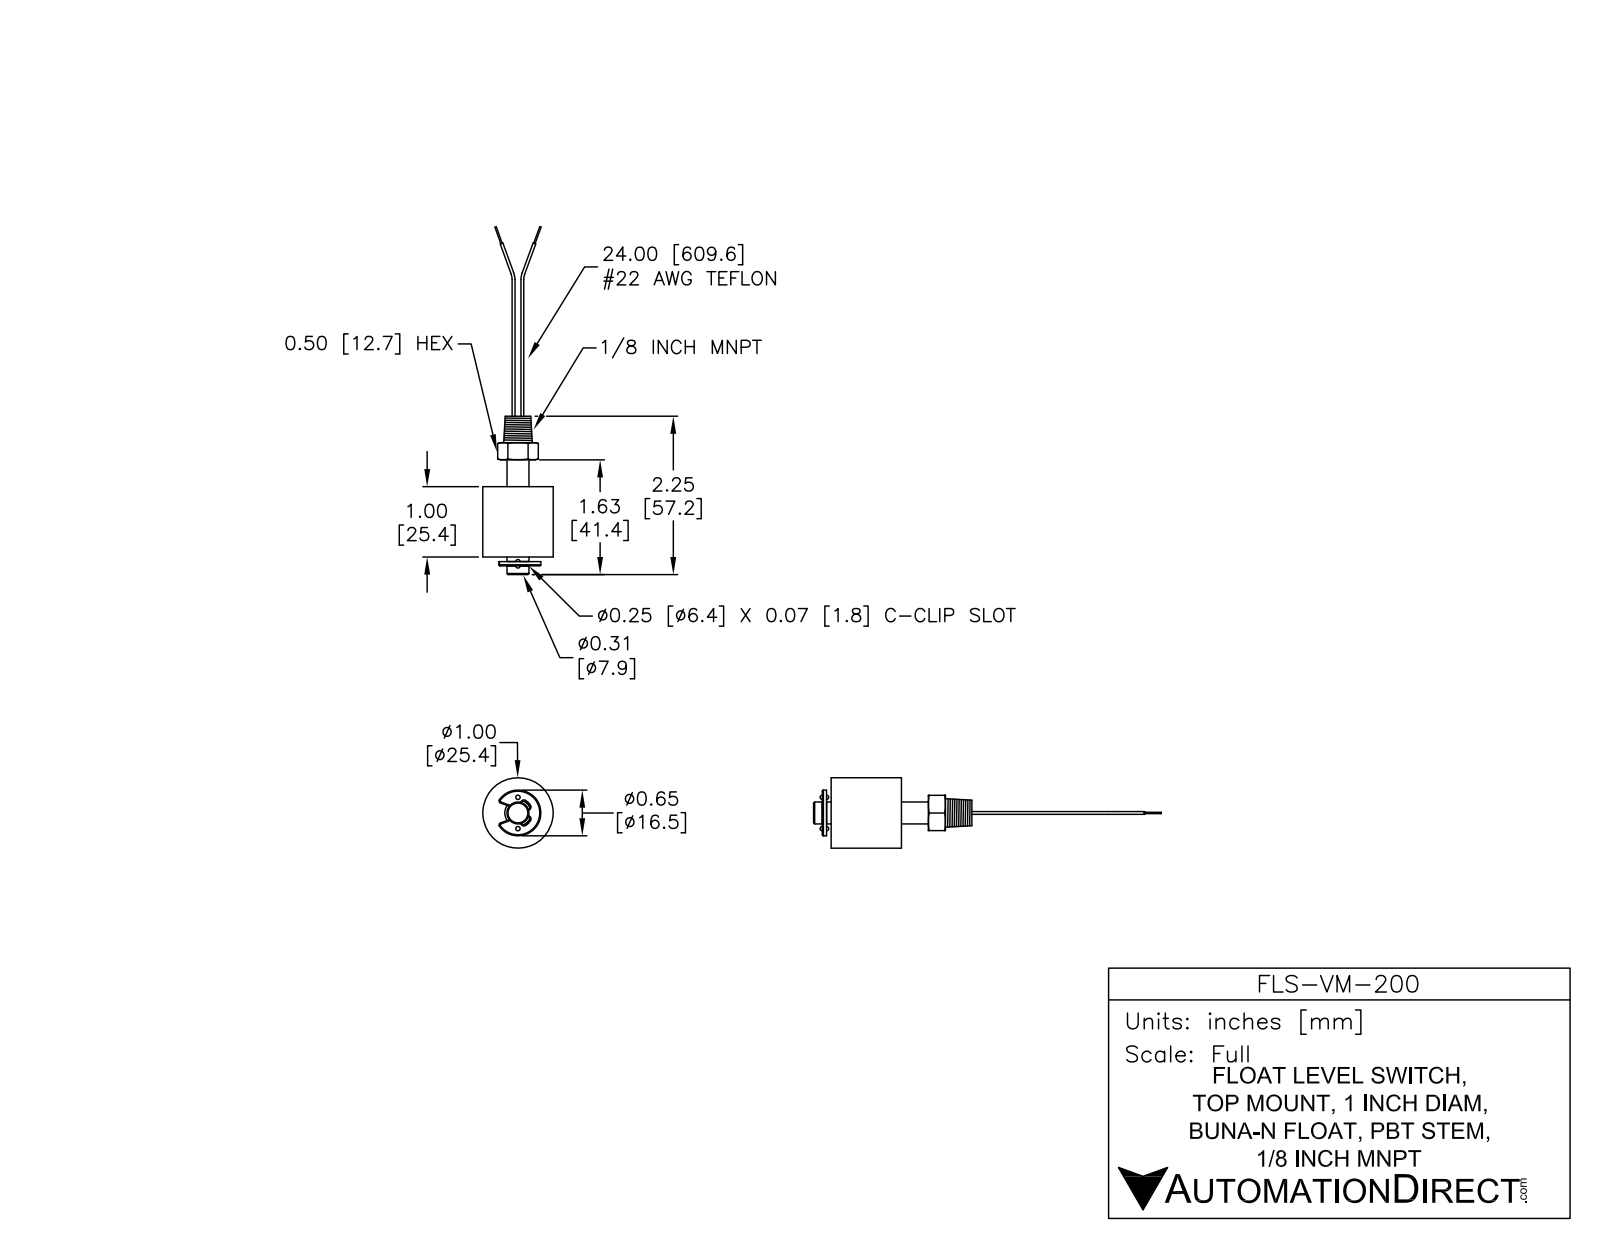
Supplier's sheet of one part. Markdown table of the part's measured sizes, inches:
| quantity | value |
| --- | --- |
| part name | FLS-VM-200 |
| STEP written by | SolidWorks 2013 (AUTOMOTIVE_DESIGN) |
| units | inches |
| bodies | 6 solids, 95 faces (33 planar, 46 cylindrical, 16 other) |
| overall size | 4.984 × 1 × 1 |
| volume | 0.928 in³ |
| surface area | 10.44 in² |
| round holes (diameter × count) | 0.38 × 1 |
| round bosses / shafts (diameter × count) | 0.04 × 4, 0.02 × 2, 1 × 1, 0.65 × 1, 0.313 × 1, 0.313 × 1, 0.25 × 1 |
| partial cylindrical surfaces (radius × count) | 0.031 × 8, 0.016 × 4, 0.128 × 1, 0.193 × 1 |
| main face-to-face distances | 1, 1.378, 0.378, 0.128, 1.128, 1.506, 0.06, 0.067, 1.067, 1.446 |
